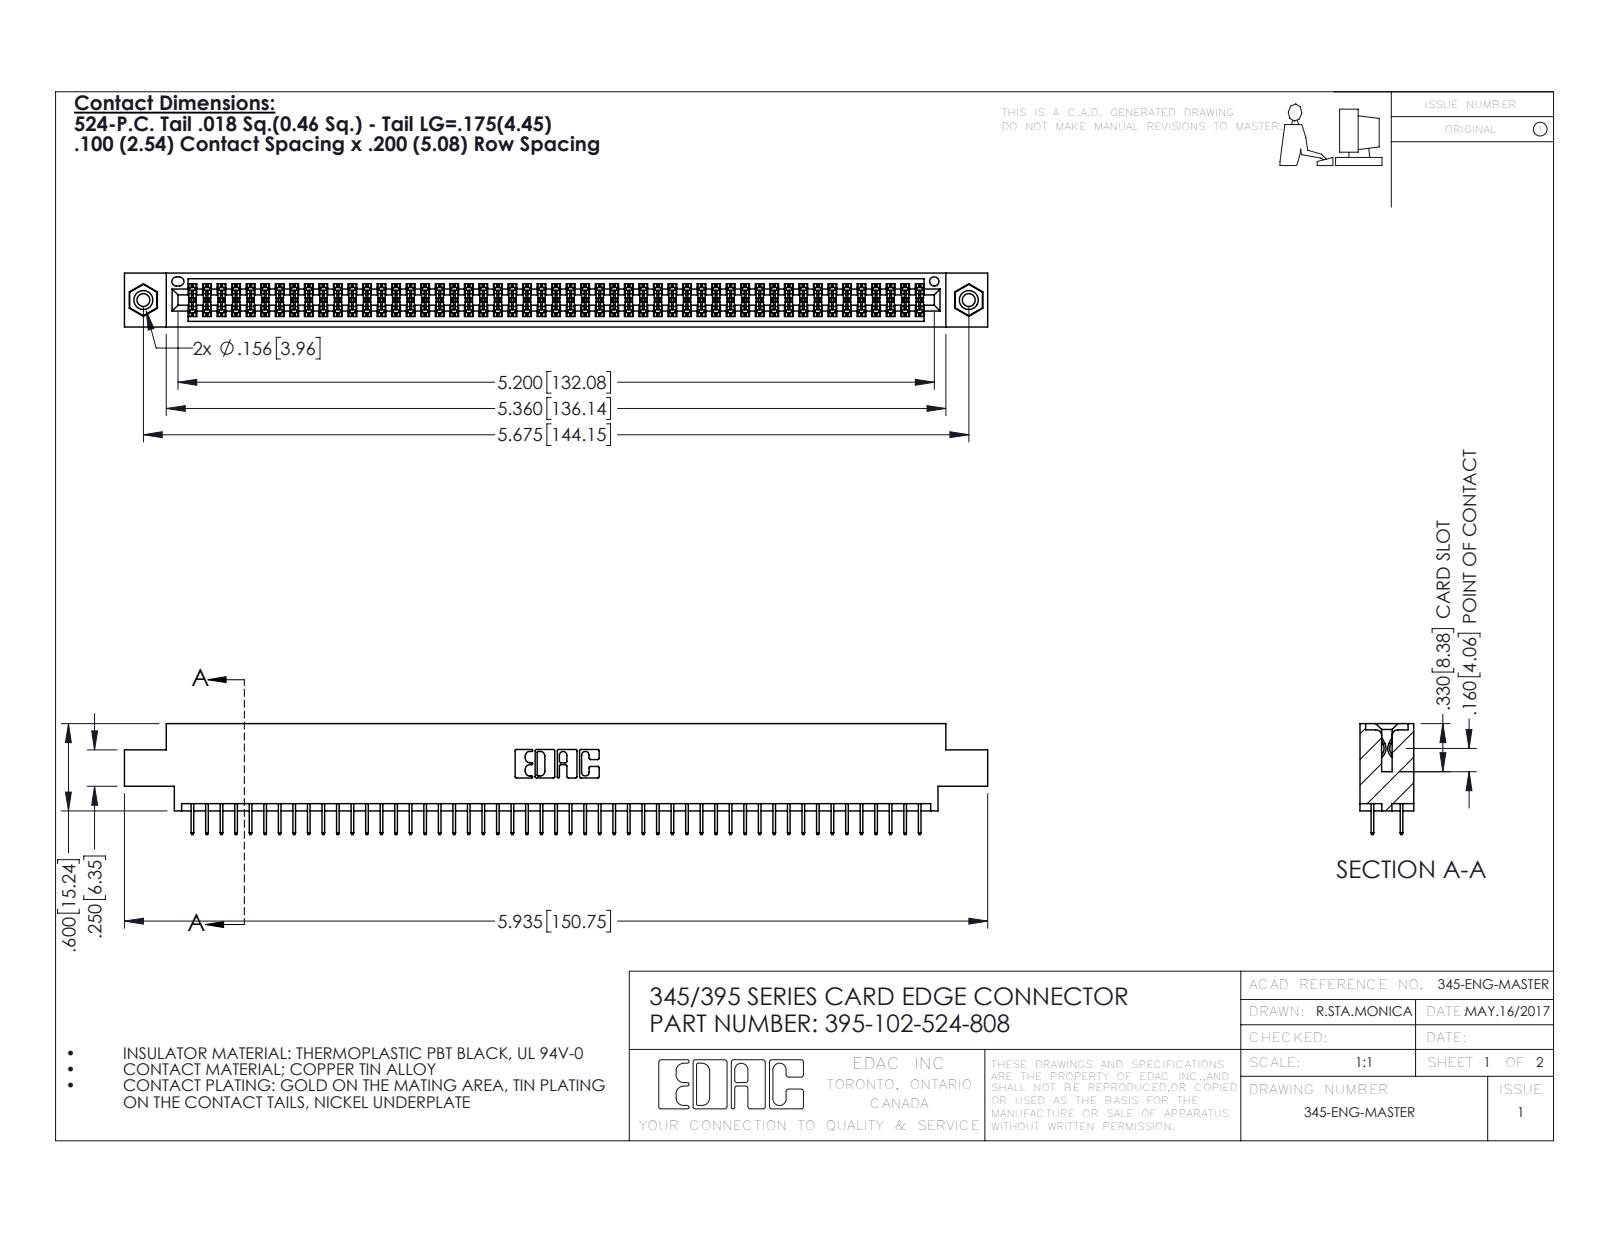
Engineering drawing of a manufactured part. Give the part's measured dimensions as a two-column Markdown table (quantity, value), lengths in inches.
| quantity | value |
| --- | --- |
| part name | 345-292-001_345-293-124; 395-102-524-808; 345 Part_0.170 Offset - 0.156 Dia-TI; 345-250-001_345-250-003-102 |
| STEP written by | SolidWorks 2016 (CONFIG_CONTROL_DESIGN) |
| units | inches |
| bodies | 105 solids, 5698 faces (4094 planar, 1588 cylindrical, 16 other) |
| overall size | 5.935 × 0.762 × 0.37 |
| volume | 0.882 in³ |
| surface area | 33 in² |
| round holes (diameter × count) | 0.089 × 2, 0.125 × 2, 0.156 × 2, 0.064 × 1 |
| round bosses / shafts (diameter × count) | 0.155 × 2 |
| partial cylindrical surfaces (radius × count) | 0.006 × 153, 0.01 × 22, 0.007 × 6, 0.031 × 6, 0.026 × 3, 0.014 × 2, 0.019 × 2, 0.022 × 2 |
| main face-to-face distances | 0.072, 0.298, 0.37, 0.2, 0.098, 0.272, 0.025, 0.225, 0.072, 0.175 |
| hole center spacings | 0.27, 5.439, 5.675 |
